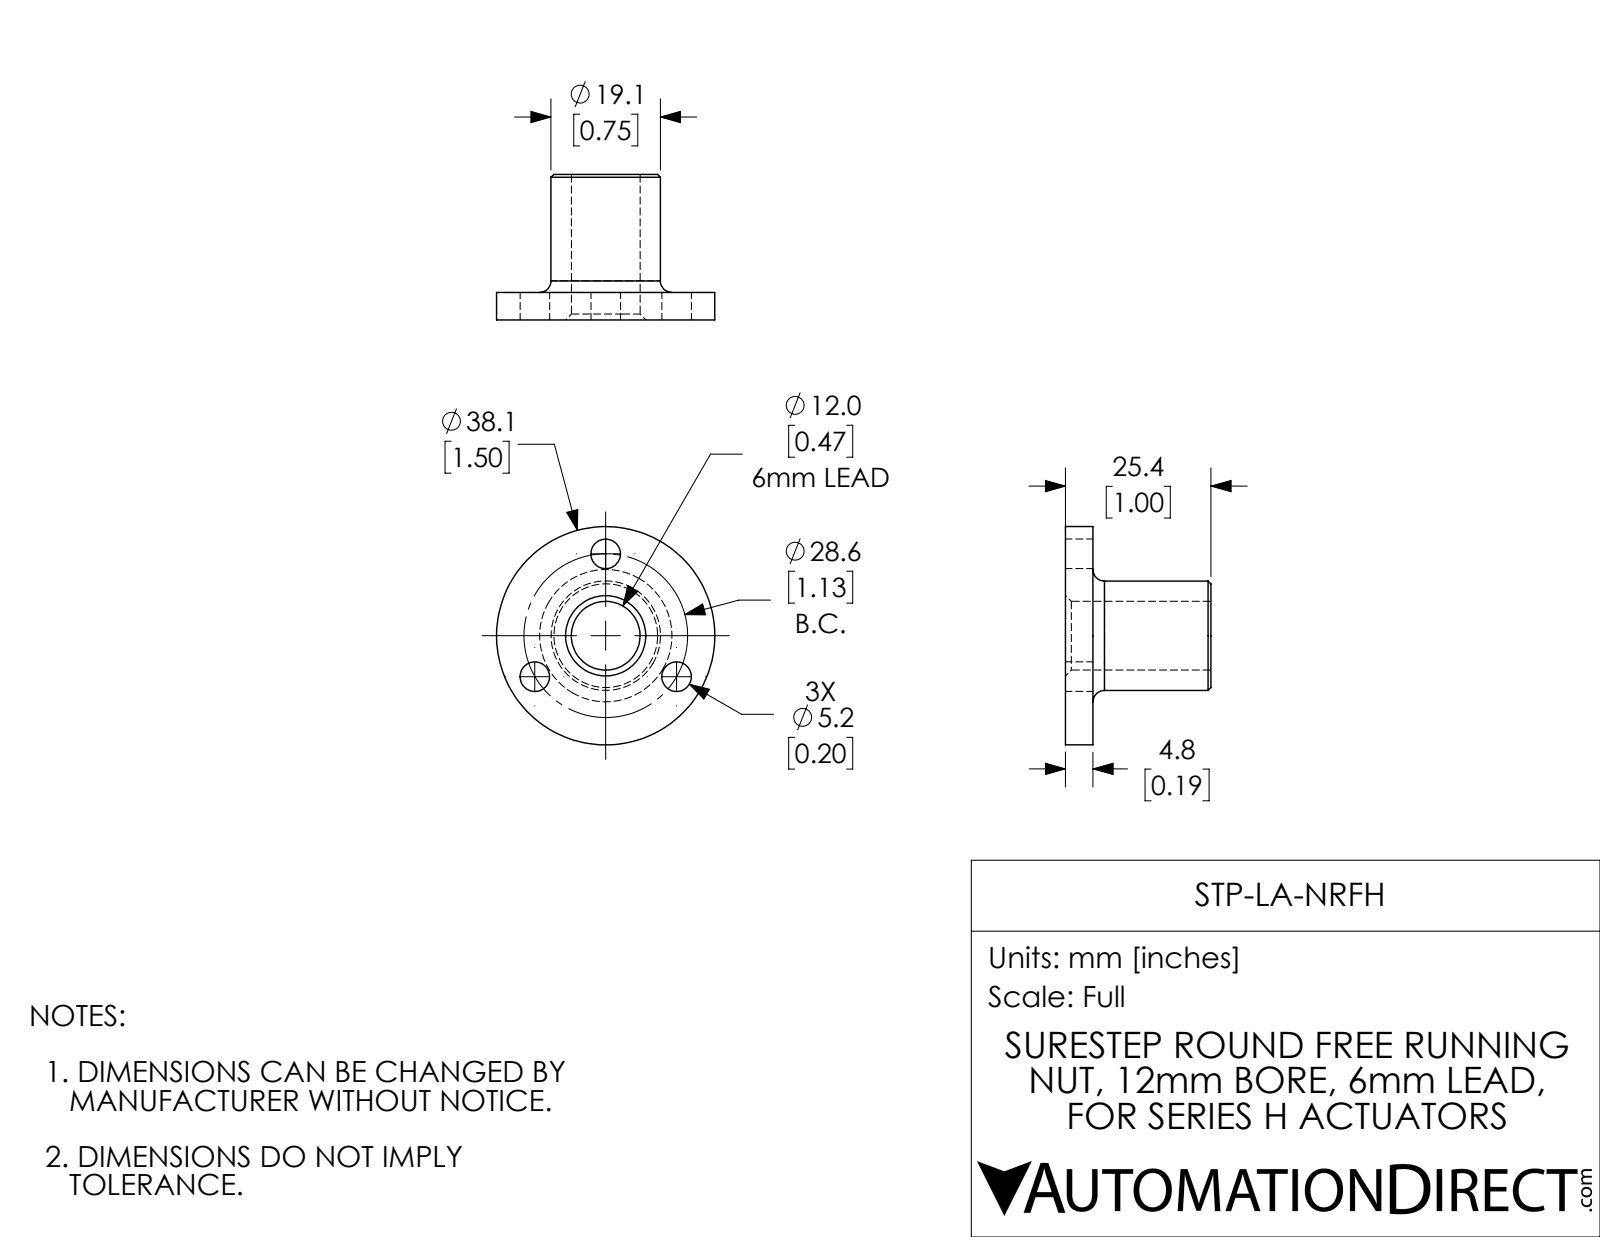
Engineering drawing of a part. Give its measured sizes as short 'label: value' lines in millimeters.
name: STP-LA-NRFH
written by: SolidWorks 2017 (AUTOMOTIVE_DESIGN)
unit: mm
bodies: 1 solid, 21 faces (3 planar, 12 cylindrical, 6 other)
size: 38.1 × 38.1 × 25.4
volume: 8 230 mm³; area: 4 842 mm²
holes: 3× ⌀5.2, 1× ⌀12
bosses: 1× ⌀38.1, 1× ⌀19.1
face distances: 4.8, 20.6, 25.4
hole spacings: 14.3, 24.7, 14.3, 24.7
